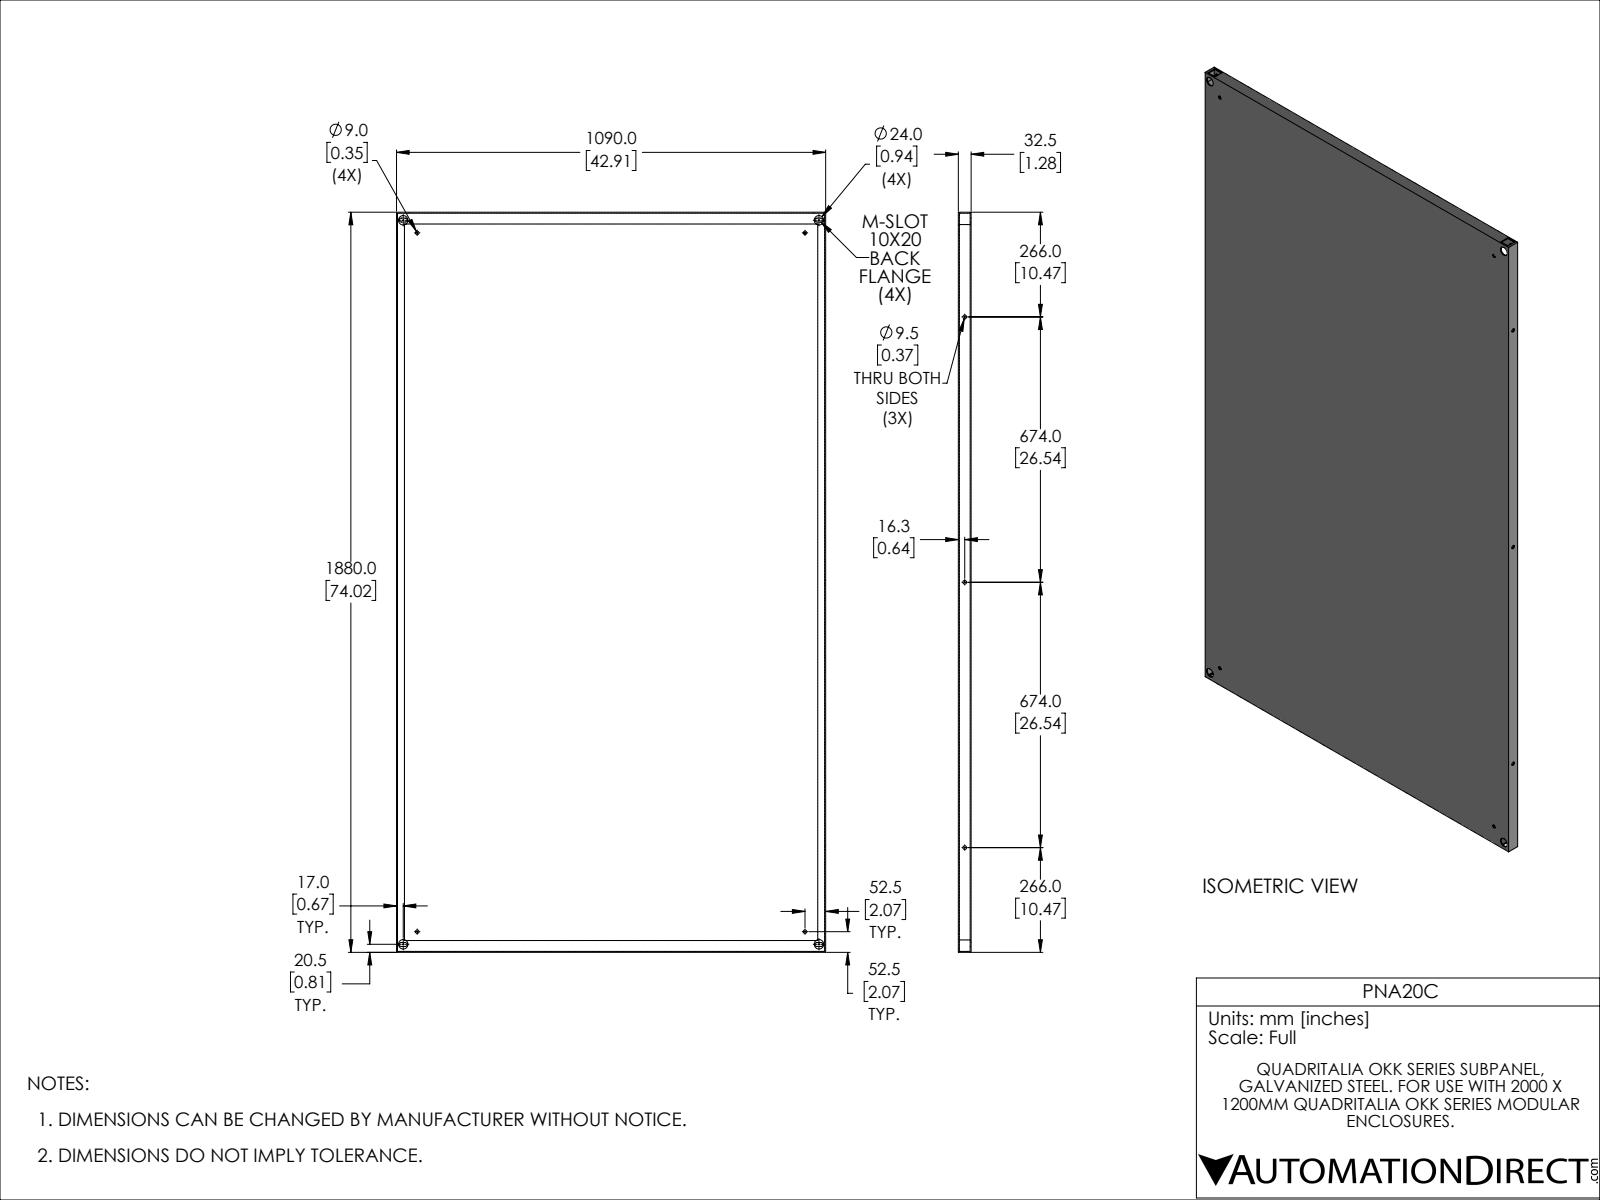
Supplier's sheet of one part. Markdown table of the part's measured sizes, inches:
| quantity | value |
| --- | --- |
| part name | PNA20C |
| STEP written by | SolidWorks 2021 (CONFIG_CONTROL_DESIGN) |
| units | inches |
| bodies | 1 solid, 70 faces (48 planar, 22 cylindrical, 0 other) |
| overall size | 74.016 × 42.913 × 1.28 |
| volume | 357.7 in³ |
| surface area | 7 296 in² |
| round holes (diameter × count) | 0.354 × 4, 0.945 × 4, 0.374 × 3 |
| partial cylindrical surfaces (radius × count) | 0.197 × 8 |
| main face-to-face distances | 0.098, 1.181, 1.28, 1.083, 42.815, 42.913, 73.917, 42.717, 74.016, 73.819 |
| hole center spacings | 1.881, 40.197, 71.156, 81.703, 26.535, 38.78, 41.575, 69.882 |
